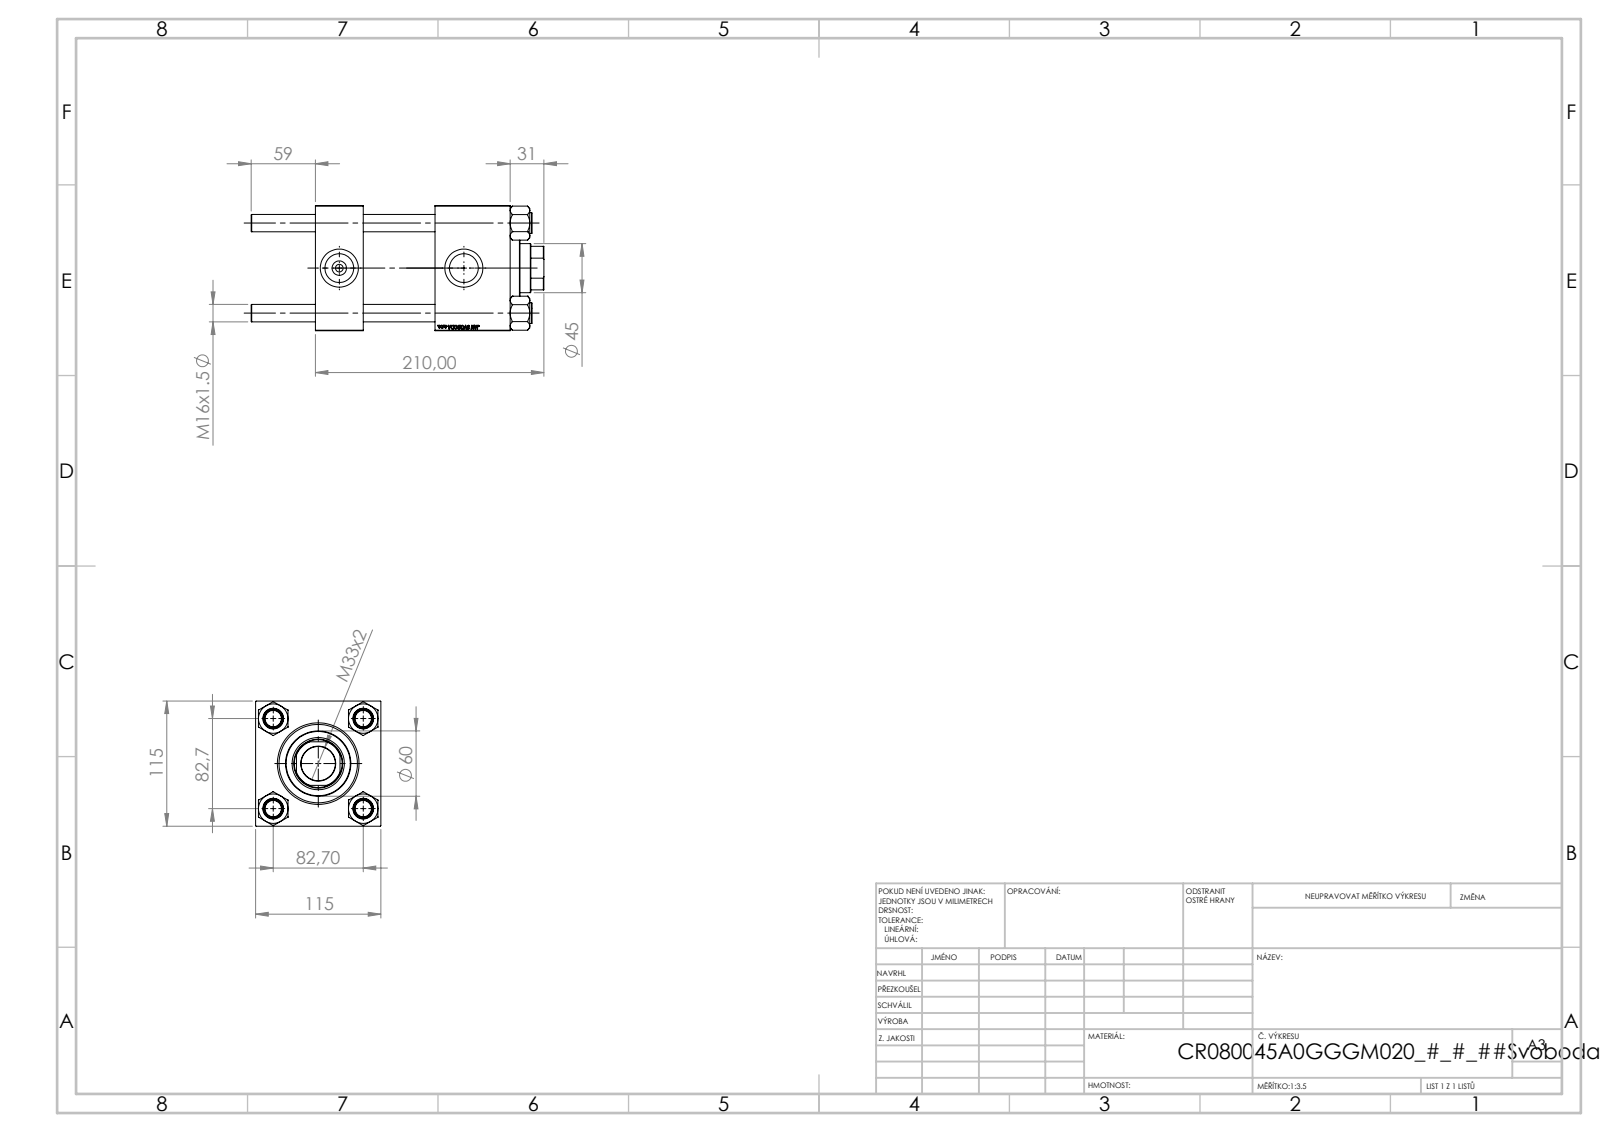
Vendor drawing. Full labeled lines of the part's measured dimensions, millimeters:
Part name (STEP PRODUCT): V215_VC_A; V215CR_BODY_A; V215CR_VCP; NUT_M5 (+1 more)
STEP written by: SolidWorks 2019 (CONFIG_CONTROL_DESIGN)
Units: millimetres
Bodies: 11 solids, 1182 faces (567 planar, 79 cylindrical, 536 other)
Overall size (bounding box): 269 × 115 × 115
Volume: 1 896 000 mm³ · Surface area: 300 850 mm²
Round holes (diameter × count): ⌀16 ×4, ⌀7 ×2, ⌀26.44 ×2, ⌀35 ×2, ⌀31.5 ×1, ⌀45 ×1, ⌀48 ×1, ⌀61 ×1, ⌀72 ×1, ⌀80 ×1
Round bosses / shafts (diameter × count): ⌀19 ×4, ⌀86 ×1, ⌀60 ×1
Partial cylindrical surfaces — rounded edges, fillets, slot ends (radius × count): R22 ×1
Main face-to-face distances: 115, 44, 179, 135, 110, 66, 69, 20, 89, 150.3
Hole centre spacings: 58.48, 82.7, 116.96, 114.44
